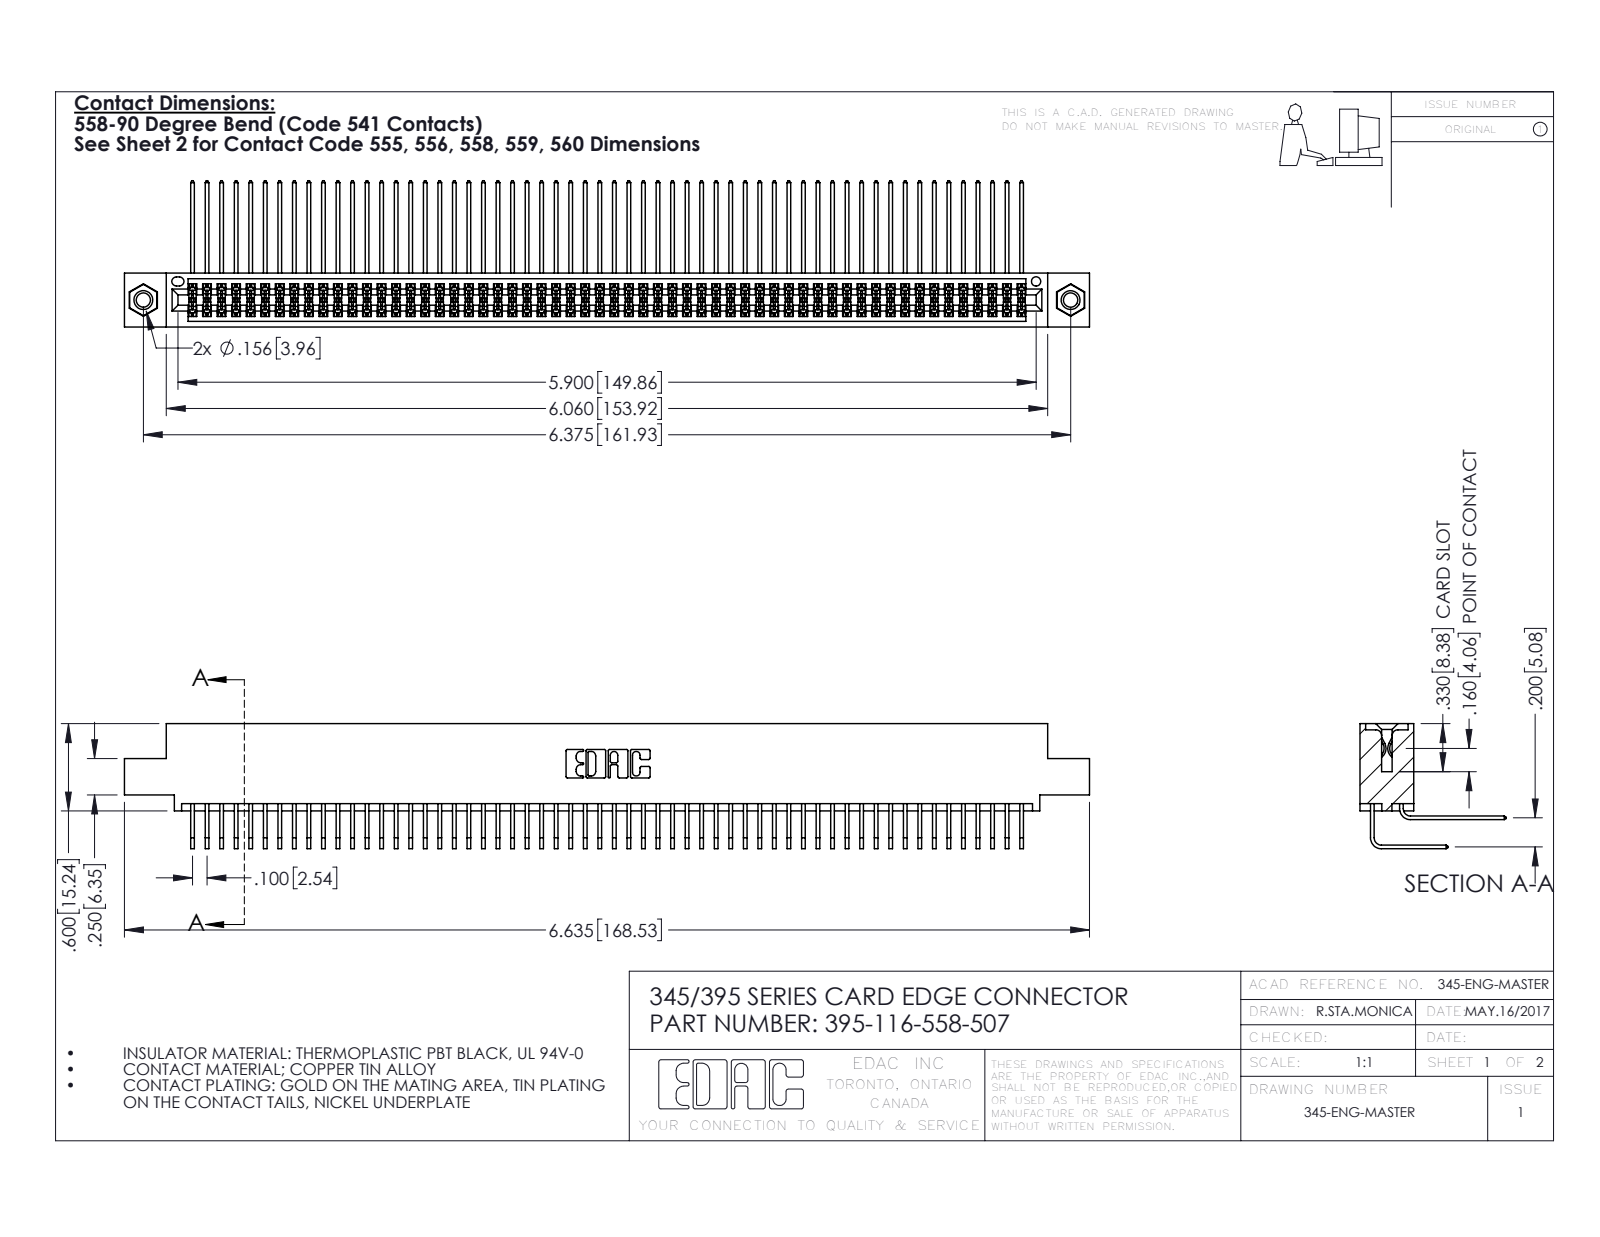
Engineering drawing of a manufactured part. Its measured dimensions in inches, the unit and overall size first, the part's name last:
Units: inches
Overall size (bounding box): 6.635 × 1.005 × 0.859
Round holes (diameter × count): ⌀0.098 ×2, ⌀0.125 ×2, ⌀0.156 ×2, ⌀0.064 ×1
Round bosses / shafts (diameter × count): ⌀0.155 ×2
Partial cylindrical surfaces — rounded edges, fillets, slot ends (radius × count): R0.006 ×174, R0.01 ×22, R0.007 ×6, R0.031 ×6, R0.026 ×3, R0.014 ×2, R0.019 ×2, R0.022 ×2
Main face-to-face distances: 0.072, 0.298, 0.2, 0.37, 0.098, 0.272, 0.025, 0.225, 0.025, 0.175
Hole centre spacings: 0.27, 6.139, 6.375
Volume: 1.044 in³ · Surface area: 44.73 in²
Bodies: 119 solids, 6222 faces (4176 planar, 2030 cylindrical, 16 other)
Part name (STEP PRODUCT): 345-250-001_345-250-005-103; 345-292-001_558 Tail - 2; 345-292-001_558 559 Tail - 1; 345 Part_0.110 Offset - 0.156 Dia-TI (+1 more)
STEP written by: SolidWorks 2016 (CONFIG_CONTROL_DESIGN)
